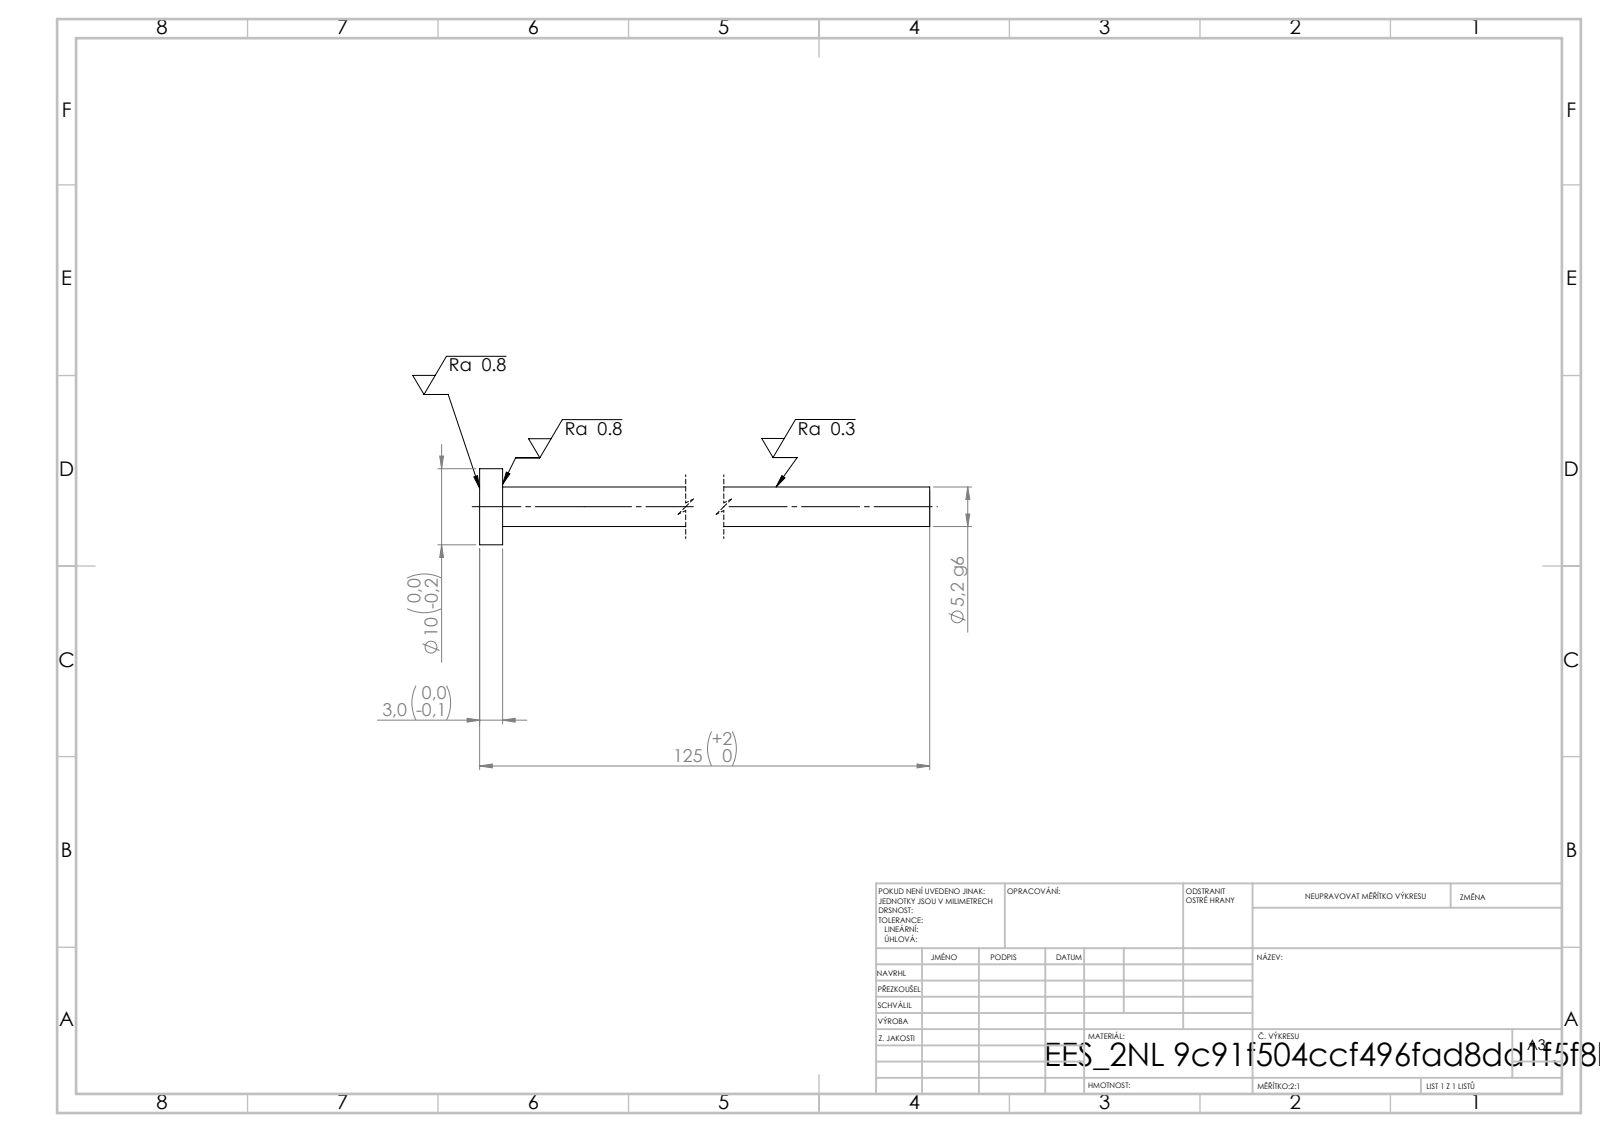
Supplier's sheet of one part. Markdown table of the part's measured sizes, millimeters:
| quantity | value |
| --- | --- |
| STEP written by | SolidWorks 2019 (CONFIG_CONTROL_DESIGN) |
| units | millimeters |
| bodies | 1 solid, 7 faces (3 planar, 4 cylindrical, 0 other) |
| overall size | 125 × 10 × 10 |
| volume | 2 827 mm³ |
| surface area | 2 244 mm² |
| round bosses / shafts (diameter × count) | 10 × 1, 5.2 × 1 |
| main face-to-face distances | 3, 125, 122 |
